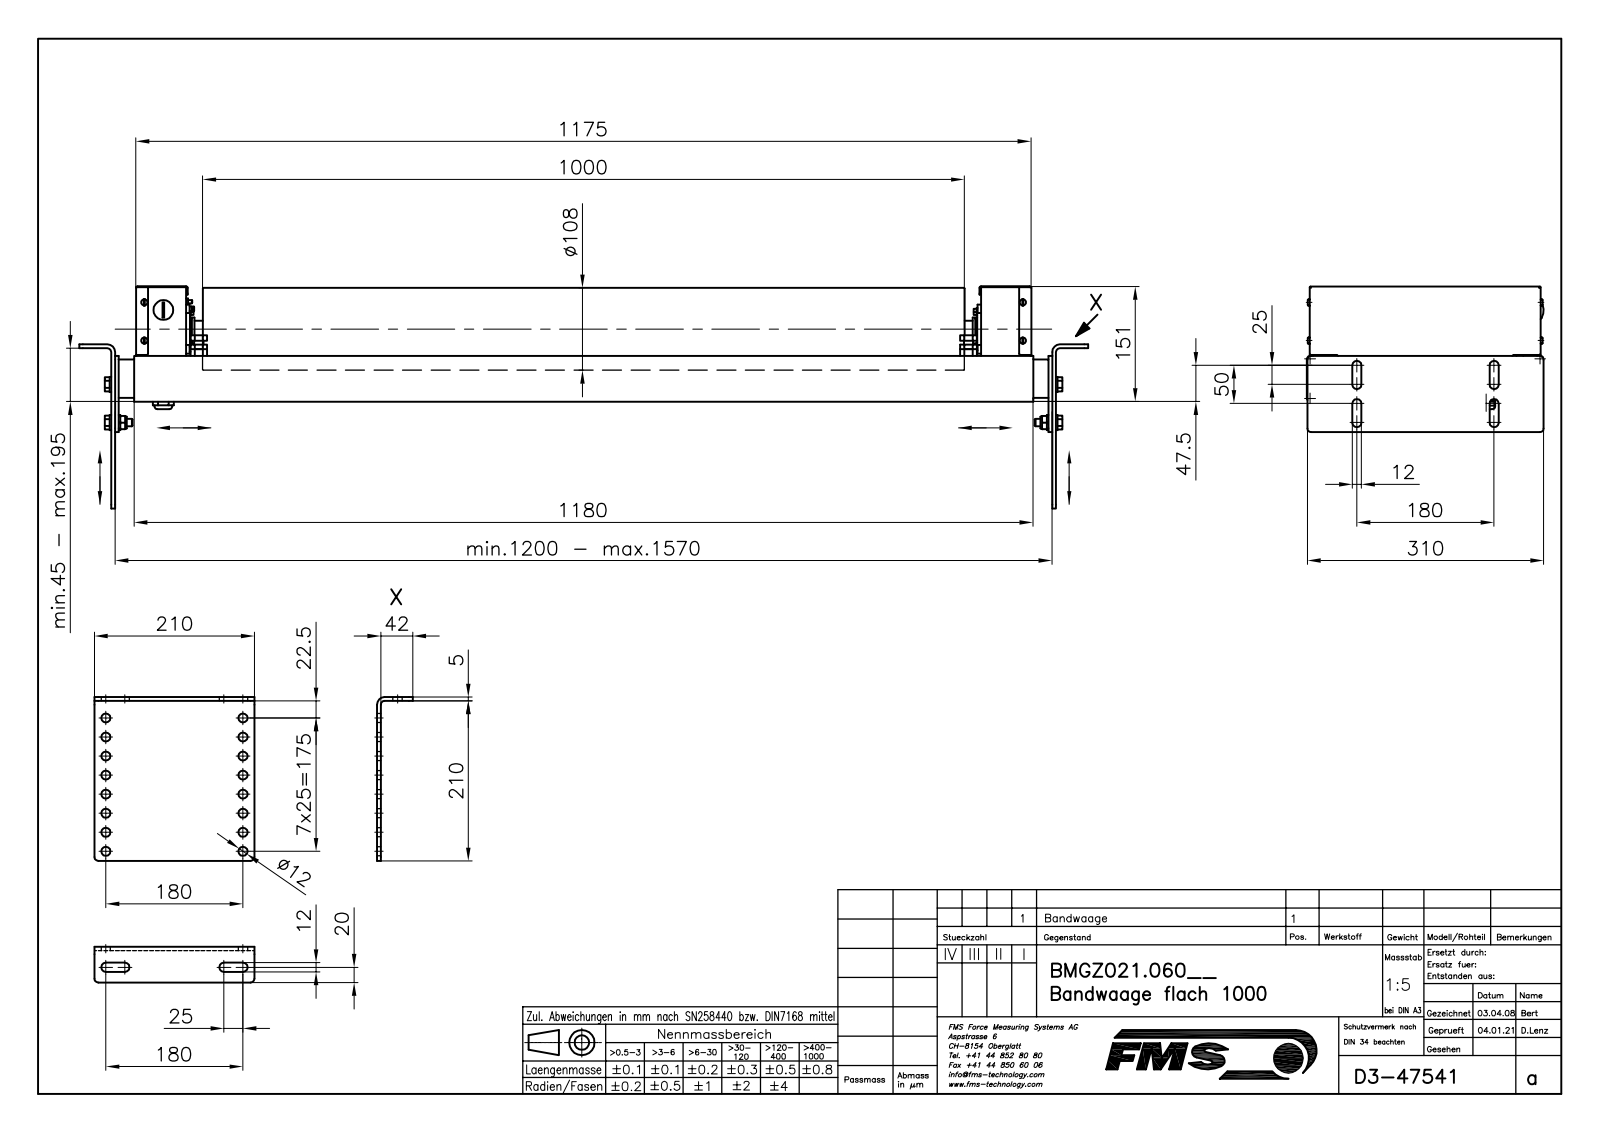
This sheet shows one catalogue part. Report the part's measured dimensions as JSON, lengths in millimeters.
{"part_name": "B47541_STP; B49646; B46966; TEIL1 (+8 more)", "step_written_by": "Mechanical Desktop 2009 (CONFIG_CONTROL_DESIGN)", "units": "millimeters", "bodies": {"solids": 136, "faces": 2360, "planar": 1273, "cylindrical": 820, "other": 267}, "overall_size": [1324, 310.5, 291], "volume_mm3": 13240000, "surface_area_mm2": 2685000, "round_holes": [[12, 17], [5, 6], [3.5, 4], [4.9, 4], [6.4, 4], [8.68, 4], [8.75, 4], [10, 4], [10.5, 4], [10.68, 4], [14.8, 4], [6, 3]], "round_bosses_or_shafts": [[12, 11], [8.2, 8], [4.2, 8], [20, 6], [10, 6], [5, 5], [16, 4], [11.1, 4]], "partial_cylinders_radius": [[2, 34], [1, 24], [4, 16], [5, 16], [6, 12], [3.5, 8], [2.25, 6], [0.5, 4]], "face_to_face_distances": [4, 5, 1, 270, 36, 266, 32, 56, 10, 3], "hole_center_spacings": [25, 50, 181.73, 186.82, 75, 195, 100, 180]}
